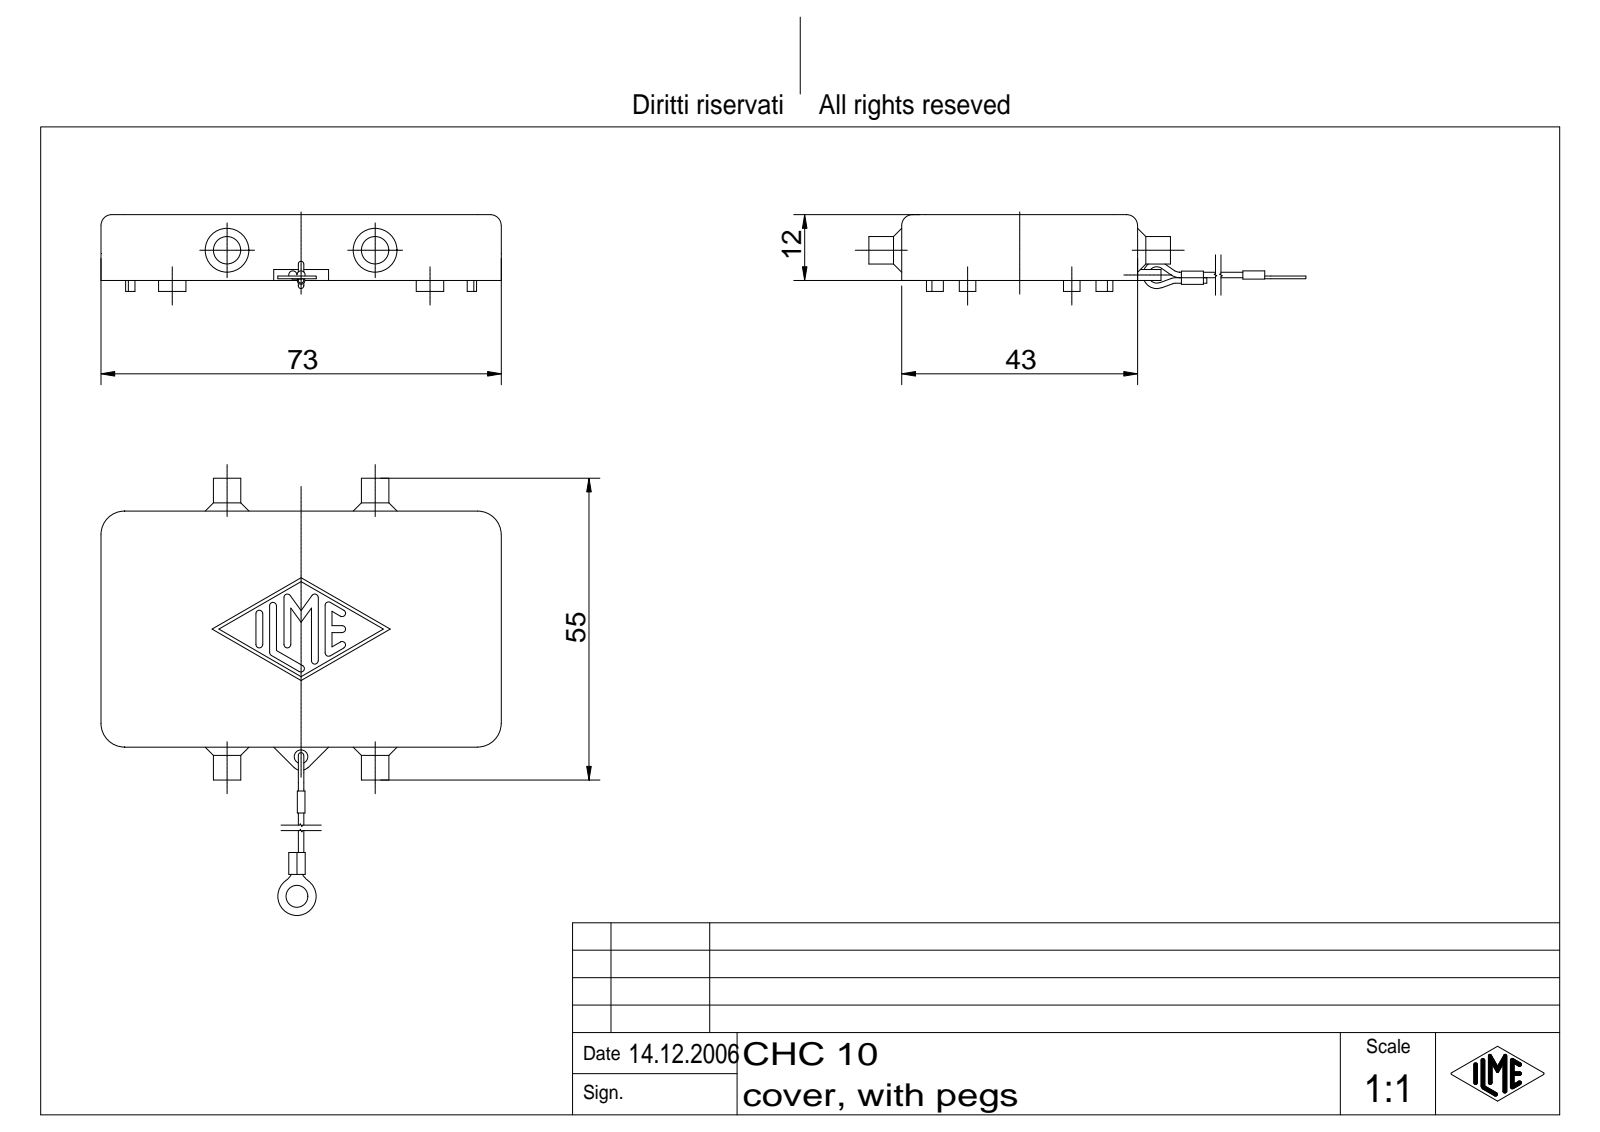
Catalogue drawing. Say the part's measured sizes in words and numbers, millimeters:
The part is named "CHC 10". Its 3-D file was written by "Autodesk Inventor 7 (AUTOMOTIVE_DESIGN)". It is 2 solids with 222 faces: 93 planar, 73 cylindrical and 56 other. Overall it measures 153.5 by 73 by 14 millimeters. Its volume is 19 059 cubic millimeters and its surface area 11 768 square millimeters. Round holes: 1 of diameter 2.5, 1 of diameter 4. Round bosses or shafts: 4 of diameter 1, 2 of diameter 5, 1 of diameter 7. Partial cylindrical surfaces (rounded edges, fillets, slot ends): 14 of radius 0.62, 8 of radius 2, 4 of radius 0.7, 4 of radius 4.3, 2 of radius 0.75, 2 of radius 1, 2 of radius 3, 1 of radius 1.75. The main face-to-face distances are 3, 4.5, 9, 12, 38.5, 43, 34, 68.5, 73, 64. The hole center spacings are 99.25.
